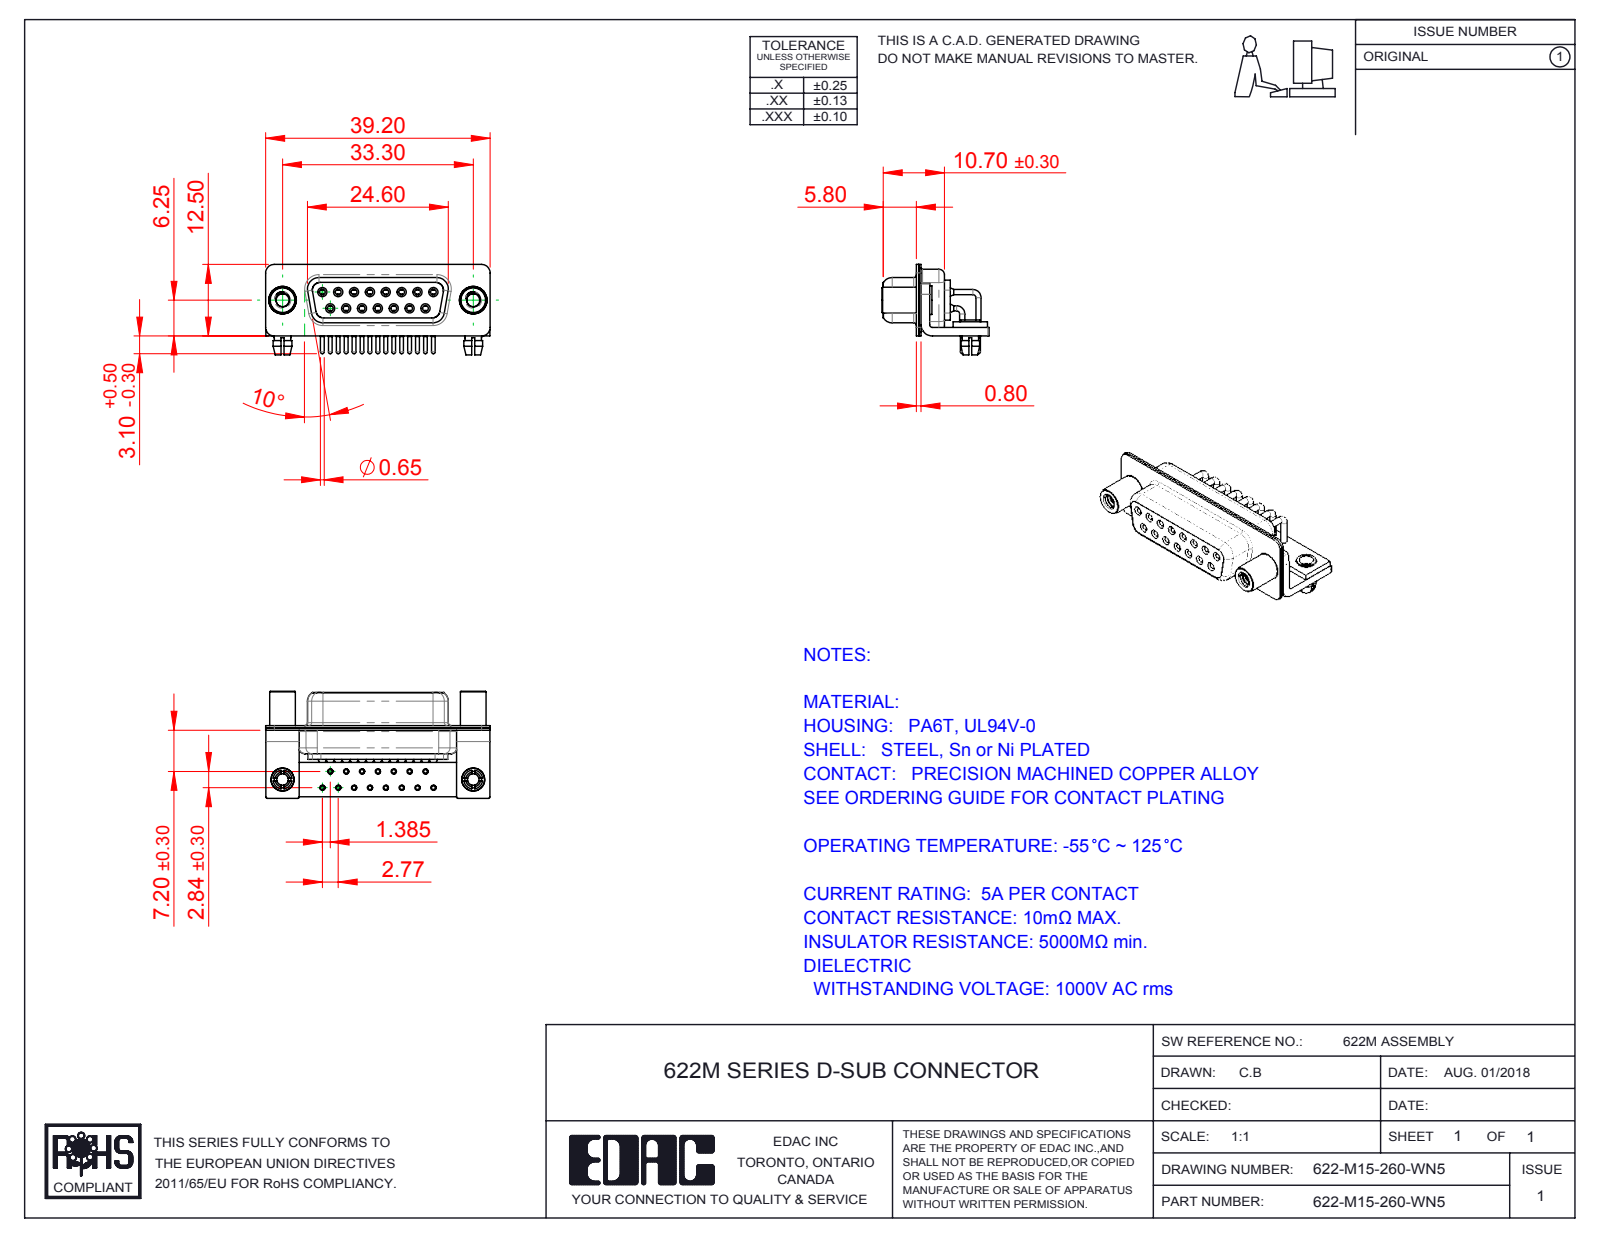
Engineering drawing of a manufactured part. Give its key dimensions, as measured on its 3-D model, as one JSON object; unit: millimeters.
{"part_name": "622-M15-260-WN5; 622M Contact Row 1; 622M Shell Rear_15 Contacts; 622M Board Lock (+6 more)", "step_written_by": "SolidWorks 2016 (CONFIG_CONTROL_DESIGN)", "units": "millimeters", "bodies": {"solids": 25, "faces": 1296, "planar": 368, "cylindrical": 608, "other": 320}, "overall_size": [39.2, 18.7, 15.8], "volume_mm3": 3146, "surface_area_mm2": 8070, "round_holes": [[2, 17], [0.9, 15], [1, 15], [1.1, 15], [1.7, 15], [1.8, 15], [2.26, 2], [2.5, 2], [3.2, 2], [4, 2], [4.8, 2]], "round_bosses_or_shafts": [[0.9, 22], [1.6, 15], [1.5, 15], [0.65, 15], [5, 2], [4.9, 2], [4.5, 2], [4, 2]], "partial_cylinders_radius": [[0.25, 16], [1.5, 16], [2, 13], [1.35, 8], [1.6, 8], [0.5, 5], [0.6, 4], [0.65, 4]], "face_to_face_distances": [0.4, 2.3, 1.9, 0.8, 9.35, 1.5, 1, 1.45, 8.95, 0.85], "hole_center_spacings": [3.16, 2.77, 5.54, 8.31, 11.08, 5.03, 5.04, 7.48]}
